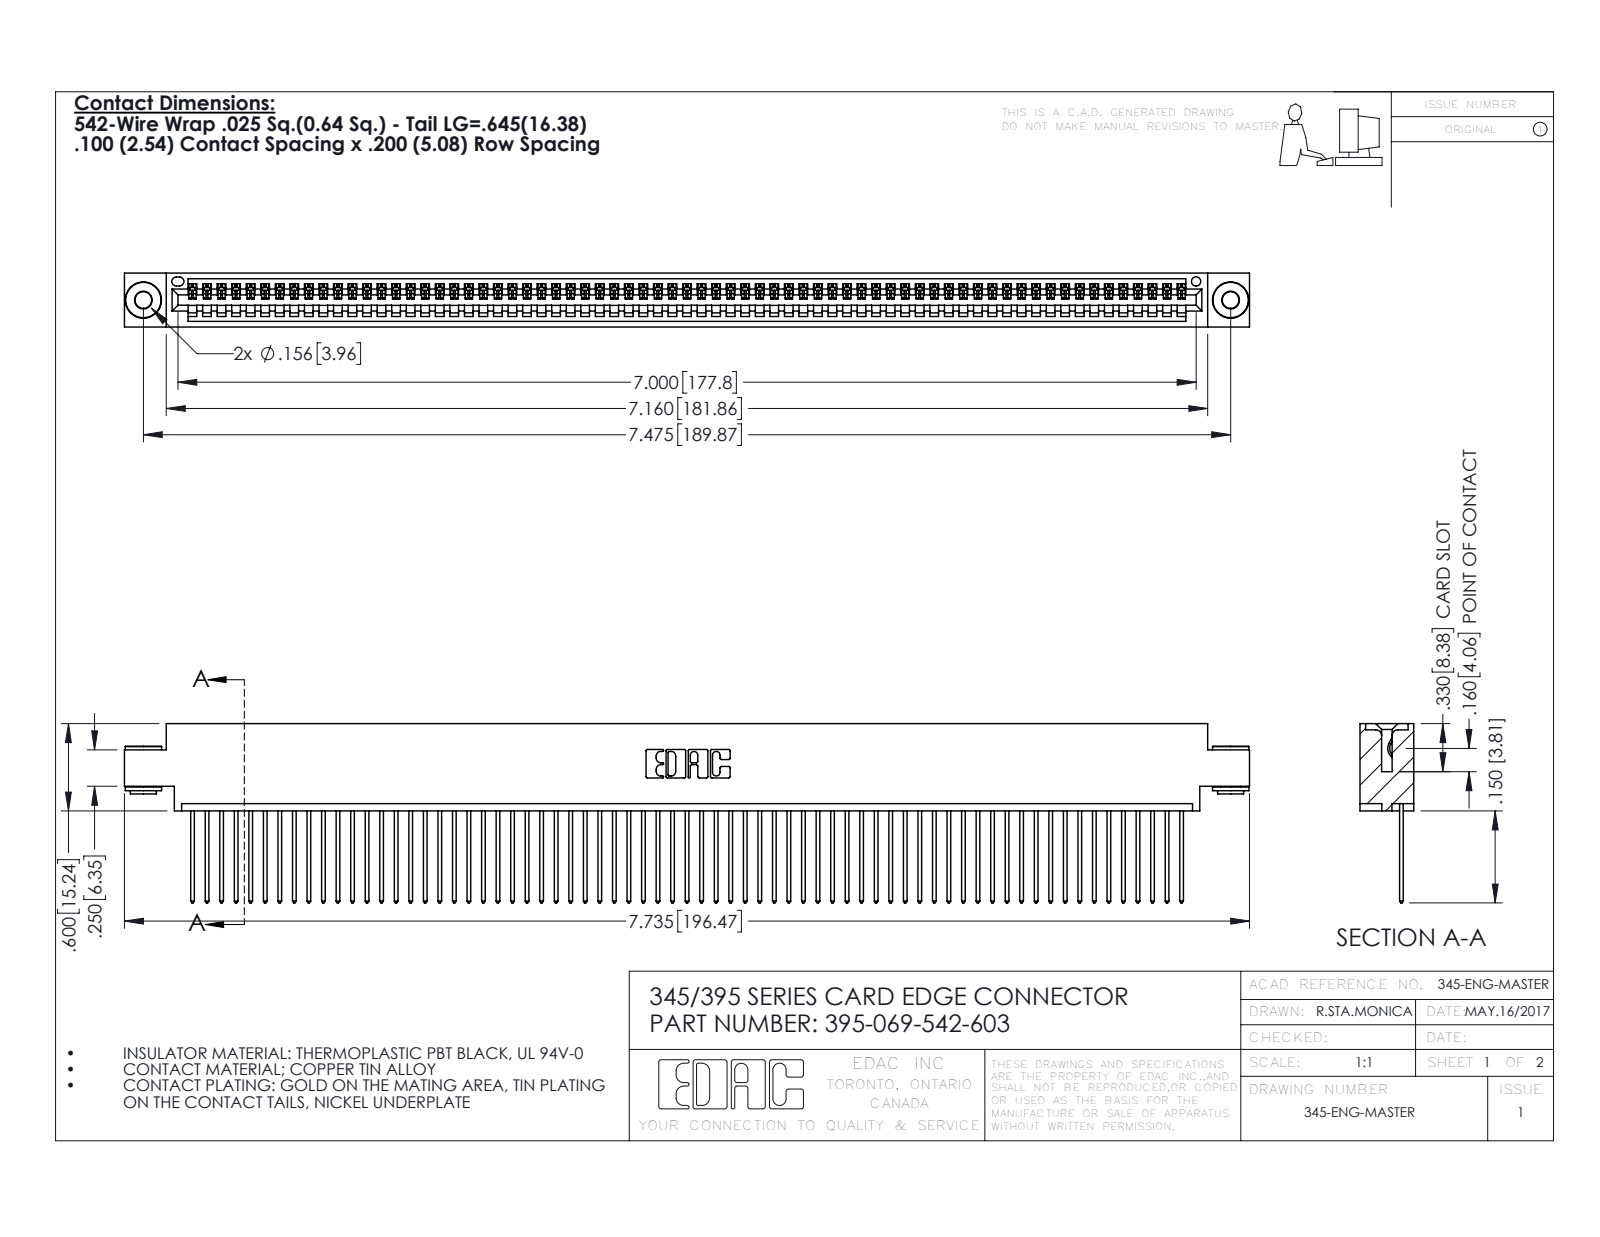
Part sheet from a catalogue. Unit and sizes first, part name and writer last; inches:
Units: inches
Overall size (bounding box): 7.735 × 1.232 × 0.37
Round holes (diameter × count): ⌀0.116 ×2, ⌀0.156 ×2, ⌀0.064 ×1
Round bosses / shafts (diameter × count): ⌀0.25 ×2, ⌀0.18 ×2, ⌀0.136 ×2
Partial cylindrical surfaces — rounded edges, fillets, slot ends (radius × count): R0.006 ×138, R0.01 ×138, R0.01 ×22, R0.007 ×6, R0.031 ×6, R0.026 ×3, R0.031 ×2, R0.04 ×2
Main face-to-face distances: 0.072, 0.298, 0.37, 0.098, 0.272, 0.025, 0.2, 0.225, 0.175, 0.149
Hole centre spacings: 0.27, 7.239, 7.475
Volume: 1.156 in³ · Surface area: 41.62 in²
Bodies: 72 solids, 4170 faces (2854 planar, 1308 cylindrical, 8 other)
Part name (STEP PRODUCT): 395-069-542-603; 345-250-002_345-250-002-102; 345-292-001_345-293-142; 345 Part_0.170 Offset - 0.156 Dia-TH
STEP written by: SolidWorks 2016 (CONFIG_CONTROL_DESIGN)
